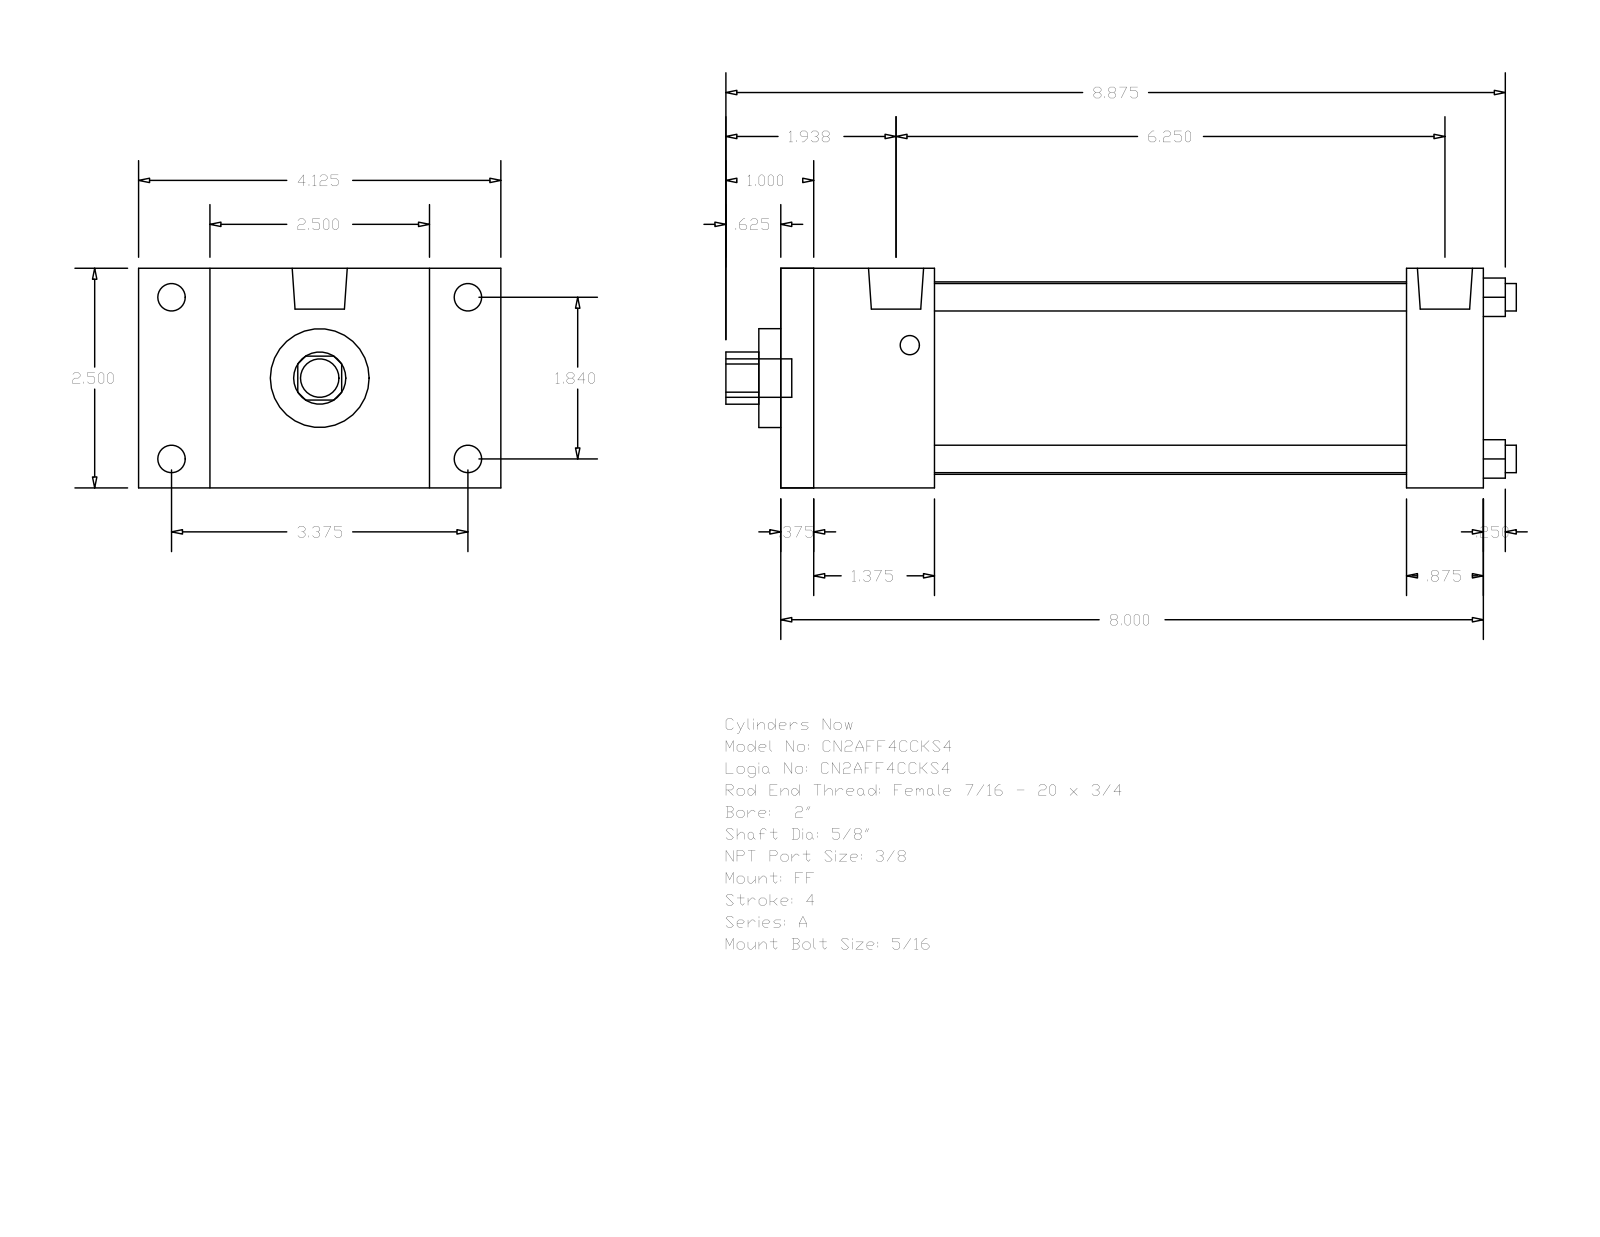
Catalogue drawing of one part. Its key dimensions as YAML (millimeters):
part_name: "A_FF__0200_0.625"
step_written_by: "GSSL Pune (CONFIG_CONTROL_DESIGN)"
units: millimeters
bodies: {solids: 0, faces: 92, planar: 64, cylindrical: 28, other: 0}
overall_size: [228.6, 104.78, 63.5]
round_holes:
  - {diameter: 7.94, count: 4}
  - {diameter: 15.88, count: 1}
  - {diameter: 28.57, count: 1}
  - {diameter: 55.63, count: 1}
round_bosses_or_shafts:
  - {diameter: 7.94, count: 4}
  - {diameter: 5.56, count: 4}
  - {diameter: 15.93, count: 2}
  - {diameter: 11.11, count: 1}
partial_cylinders:
  - {radius: 7.54, count: 1}
face_to_face_distances: [63.5, 203.19, 9.52, 193.67, 44.45, 180.97, 34.93, 171.45, 136.52, 158.74]
hole_center_spacings: [33.05, 46.74, 66.1]
